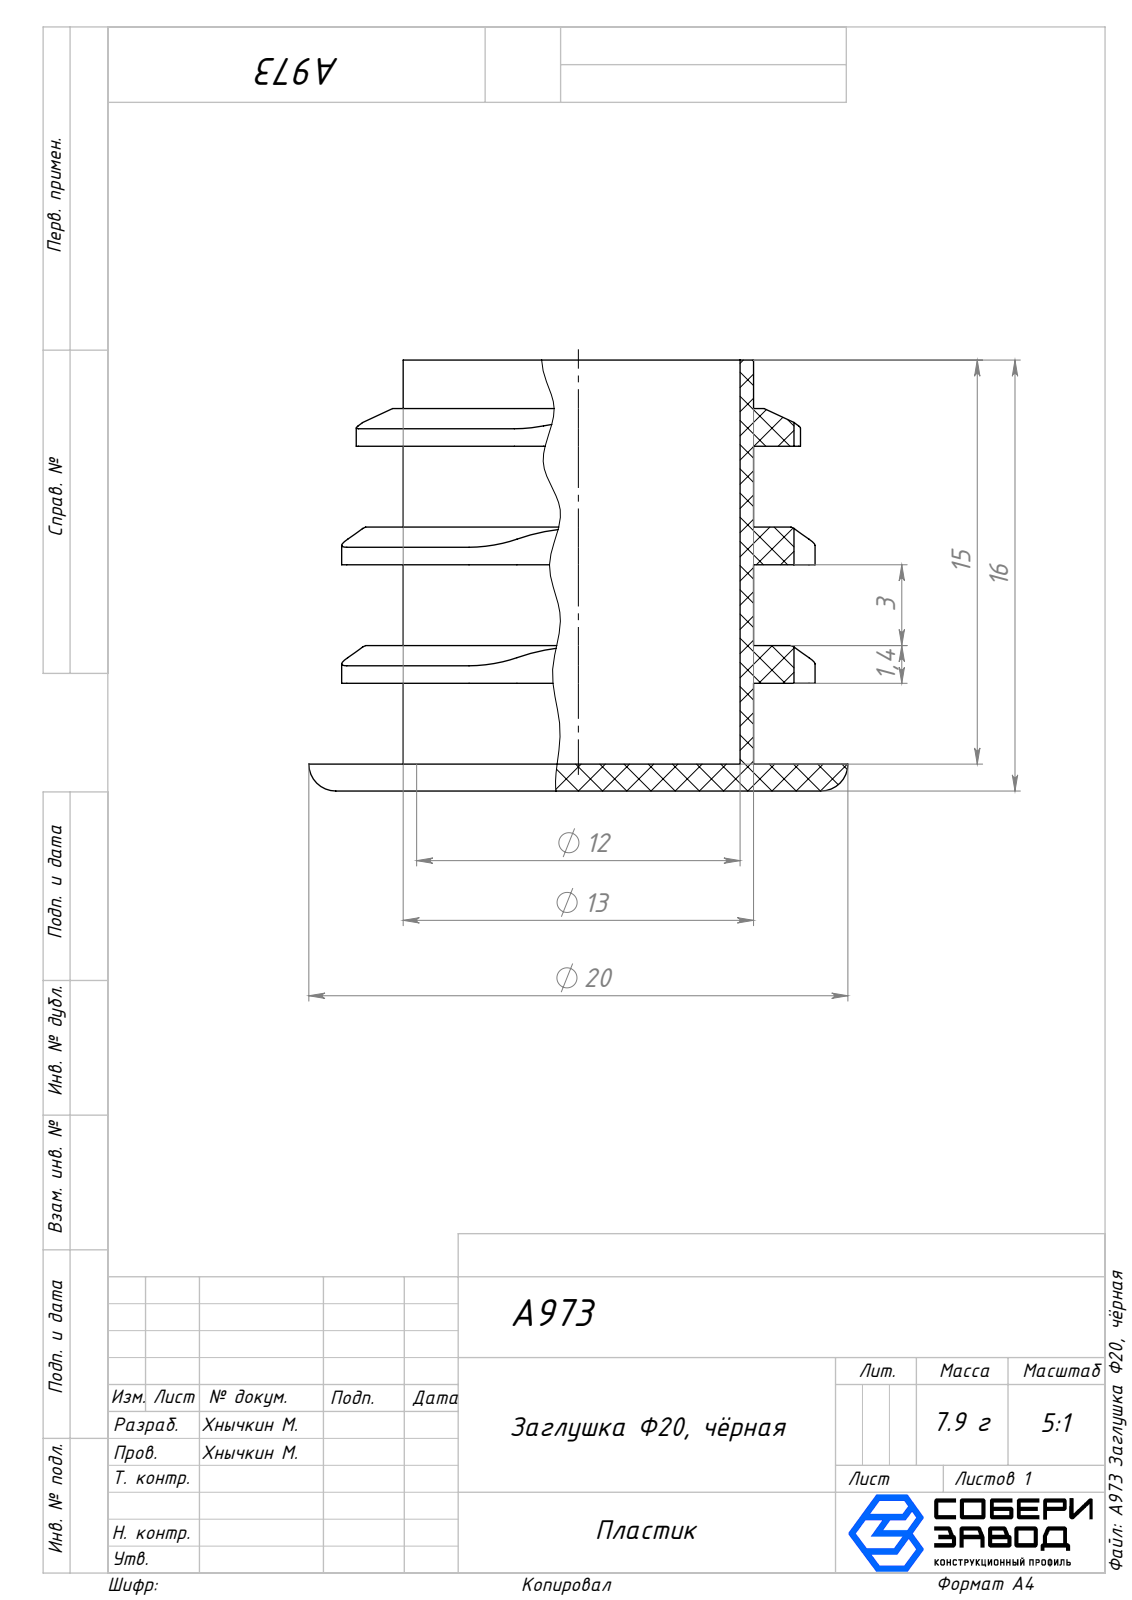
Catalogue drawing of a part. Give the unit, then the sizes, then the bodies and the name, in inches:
Units: inches
Overall size (bounding box): 0.787 × 0.787 × 0.63
Round holes (diameter × count): ⌀0.472 ×1
Round bosses / shafts (diameter × count): ⌀0.512 ×1
Partial cylindrical surfaces — rounded edges, fillets, slot ends (radius × count): R0.079 ×16, R0.195 ×4, R0.335 ×1, R0.374 ×1
Main face-to-face distances: 0.173, 0.039, 0.118, 0.291, 0.346, 0.055, 0.157, 0.331, 0.504, 0.465
Volume: 0.061 in³ · Surface area: 3.889 in²
Bodies: 1 solid, 85 faces (10 planar, 67 cylindrical, 8 other)
Part name (STEP PRODUCT): A973 Заглушка Ф20, чёрная
STEP written by: SolidWorks 2025 (AUTOMOTIVE_DESIGN)
